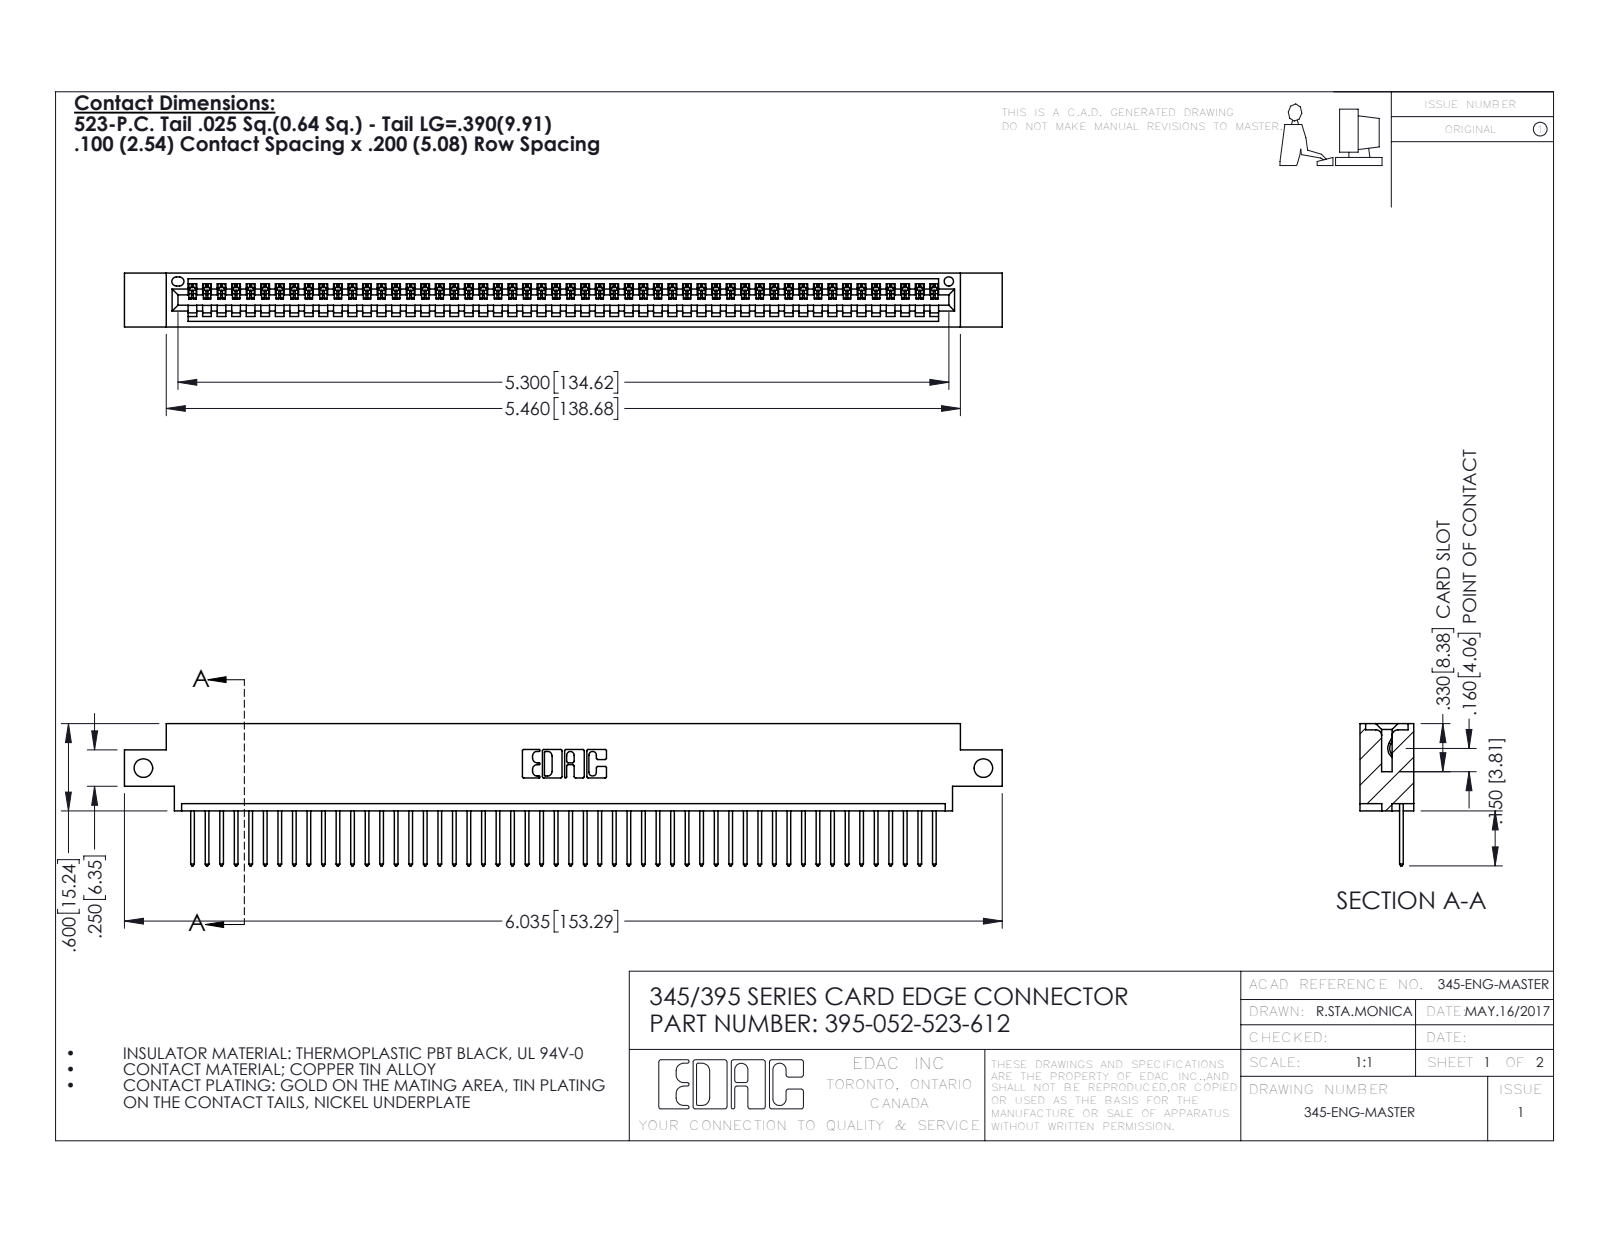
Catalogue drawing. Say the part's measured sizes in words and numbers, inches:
The part is named "345 Part_0.170 Offset - Side Mount; 345-292-001_345-293-123; 395-052-523-612". Its 3-D file was written by "SolidWorks 2016 (CONFIG_CONTROL_DESIGN)". It is 53 solids with 3146 faces: 2164 planar, 982 cylindrical and 0 other. Overall it measures 6.035 by 0.977 by 0.37 inches. Its volume is 0.88 cubic inches and its surface area 29.98 square inches. Round holes: 2 of diameter 0.128, 1 of diameter 0.064. Partial cylindrical surfaces (rounded edges, fillets, slot ends): 104 of radius 0.006, 104 of radius 0.01, 22 of radius 0.01, 6 of radius 0.007, 6 of radius 0.031, 3 of radius 0.026, 2 of radius 0.031, 2 of radius 0.04. The main face-to-face distances are 0.072, 0.298, 0.37, 0.098, 0.272, 0.025, 0.2, 0.225, 0.175, 0.149. The hole center spacings are 5.775.
